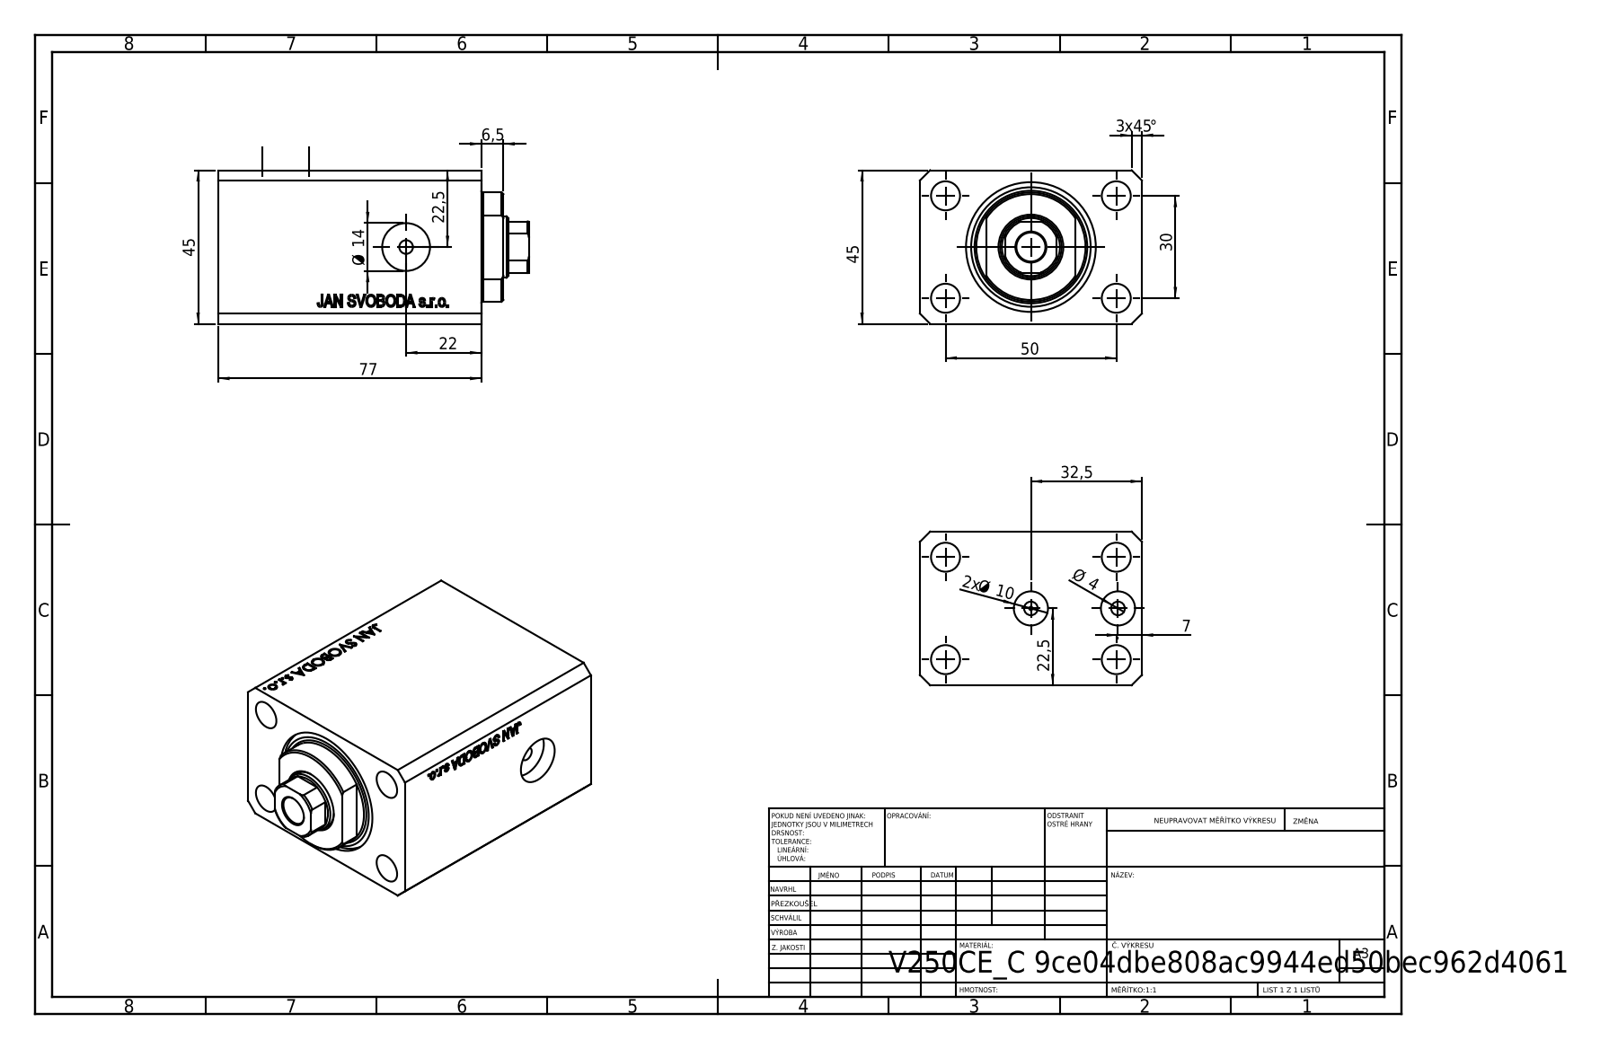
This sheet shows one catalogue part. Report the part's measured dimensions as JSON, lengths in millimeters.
{"part_name": "V250CE_C_Body; V250CE_VC_C; V250CE_C_VCP", "step_written_by": "SolidWorks 2019 (CONFIG_CONTROL_DESIGN)", "units": "millimeters", "bodies": {"solids": 3, "faces": 872, "planar": 428, "cylindrical": 50, "other": 394}, "overall_size": [90.9, 65, 45], "volume_mm3": 203496, "surface_area_mm2": 52828, "round_holes": [[8.5, 5], [4, 4], [10, 2], [14, 2], [1.25, 1], [18, 1], [25, 1], [38, 1]], "partial_cylinders_radius": [[8.5, 1], [16, 1]], "face_to_face_distances": [45, 65, 77, 51.9, 25.1, 6.9, 70.1, 73.52, 6.5, 83.5], "hole_center_spacings": [29.15, 15.01, 30, 50, 52.68, 58.31, 25.5, 33]}
